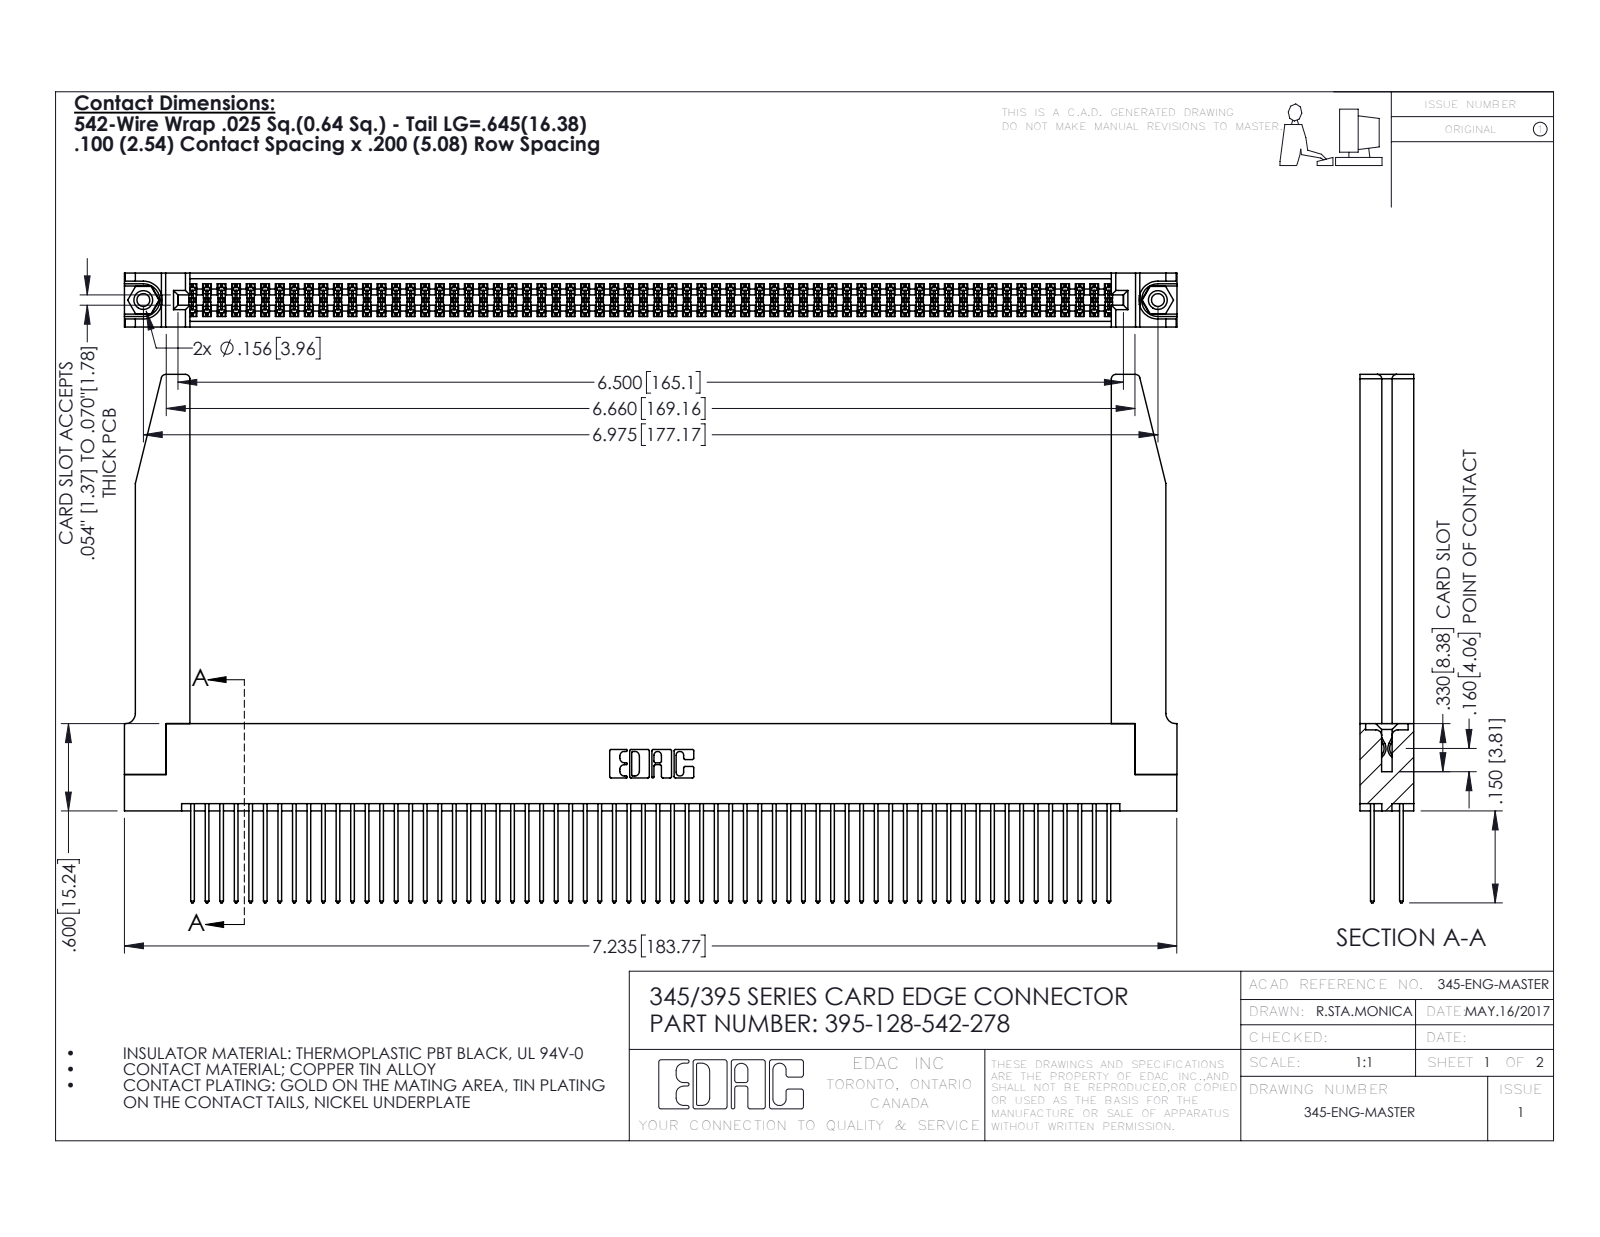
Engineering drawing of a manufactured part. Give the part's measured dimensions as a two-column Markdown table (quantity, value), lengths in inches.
| quantity | value |
| --- | --- |
| part name | 345 Part_Flush Mounting Lugs - 0.156 Dia-TH; 345-220-078_345-220-078; 395-128-542-278; 345-250-001_345-250-001-102 (+1 more) |
| STEP written by | SolidWorks 2016 (CONFIG_CONTROL_DESIGN) |
| units | inches |
| bodies | 133 solids, 6760 faces (4446 planar, 2262 cylindrical, 52 other) |
| overall size | 7.236 × 3.632 × 0.37 |
| volume | 1.613 in³ |
| surface area | 58.32 in² |
| round holes (diameter × count) | 0.089 × 2, 0.125 × 2, 0.156 × 2, 0.064 × 1 |
| round bosses / shafts (diameter × count) | 0.155 × 2 |
| partial cylindrical surfaces (radius × count) | 0.006 × 192, 0.01 × 128, 0.01 × 22, 0.03 × 8, 0.007 × 6, 0.031 × 6, 0.026 × 3, 0.014 × 2 |
| main face-to-face distances | 0.072, 0.298, 0.2, 0.37, 0.098, 0.272, 0.025, 0.225, 0.175, 0.148 |
| hole center spacings | 0.27, 6.739, 6.975 |
